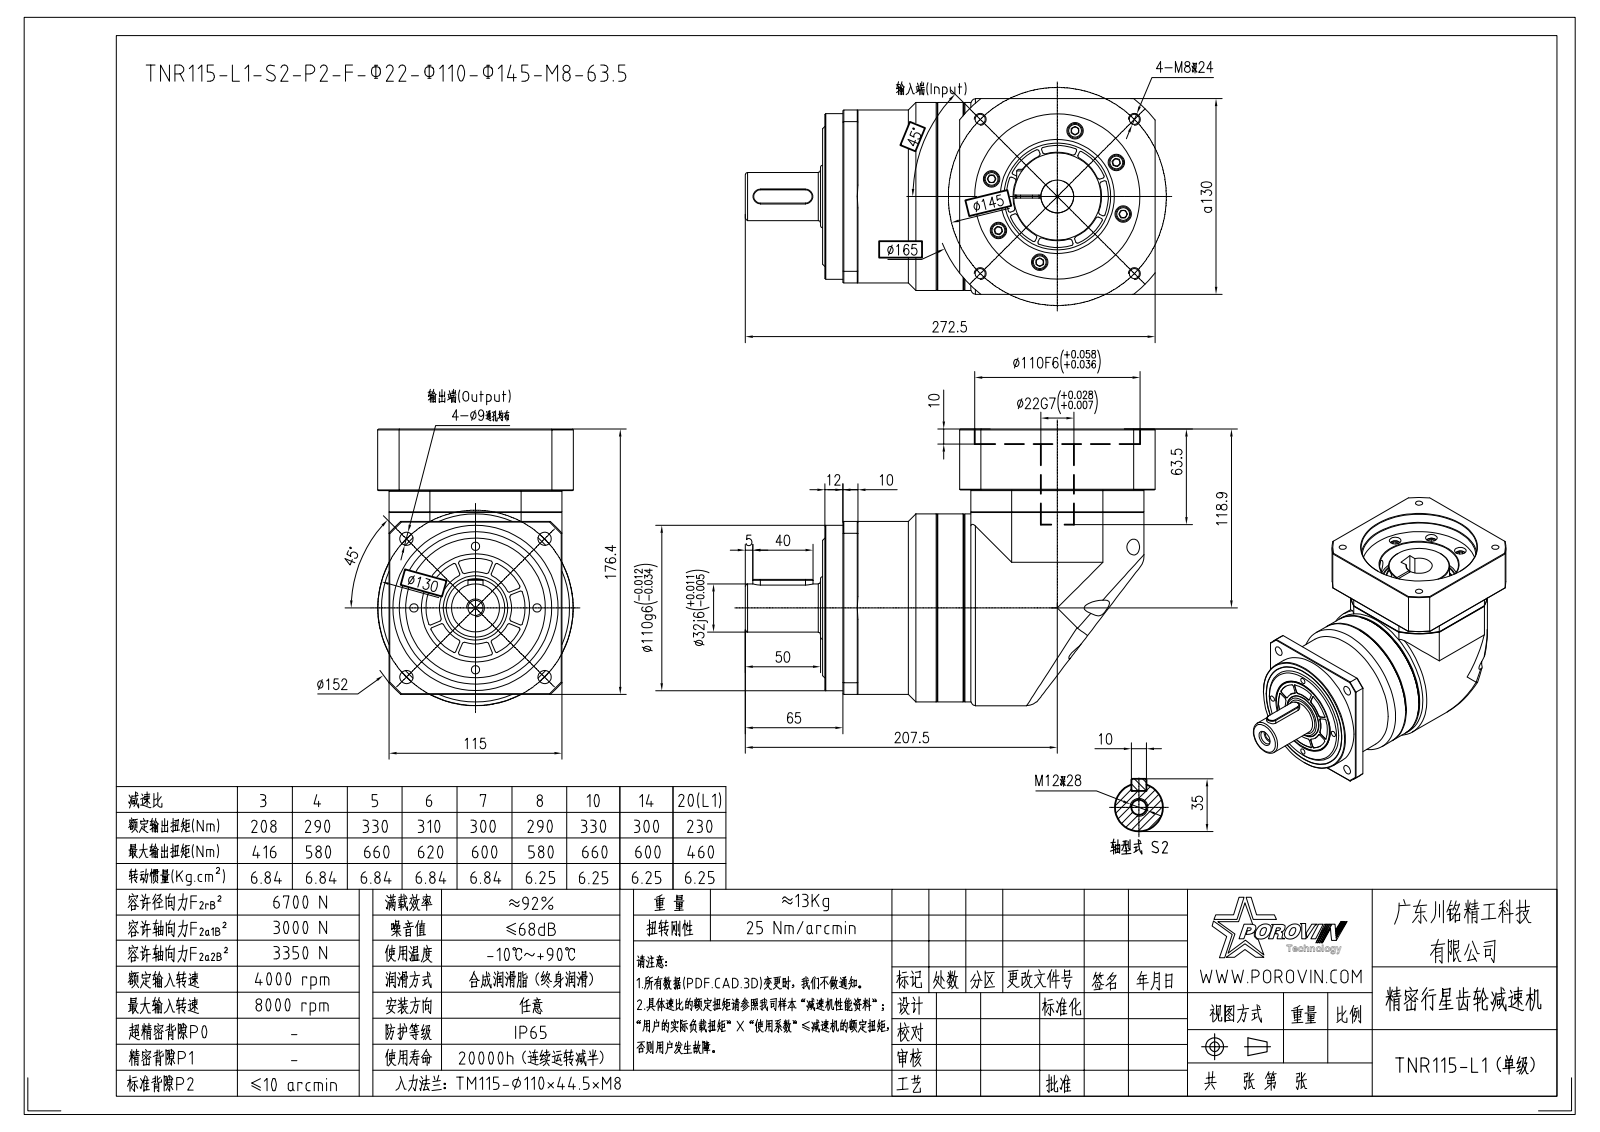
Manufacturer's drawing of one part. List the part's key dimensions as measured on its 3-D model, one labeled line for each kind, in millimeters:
Part name (STEP PRODUCT): HEXAGON_SOCKET_HEAD_CAP_SC-9367; SPRING_LOCK_WASHERS--NORMAL_TYP; HEXAGON_SOCKET_HEAD_CAP_SC-9309; HEXAGON_SOCKET_HEAD_CAP_S-29226 (+8 more)
STEP written by: CREO PARAMETRIC BY PTC INC, 2020053 (CONFIG_CONTROL_DESIGN)
Units: millimetres
Bodies: 50 solids, 1386 faces (578 planar, 557 cylindrical, 251 other)
Overall size (bounding box): 272.5 × 183.9 × 130
Volume: 2 910 000 mm³ · Surface area: 351 891 mm²
Round holes (diameter × count): ⌀6.68 ×19, ⌀6.5 ×13, ⌀11 ×12, ⌀5 ×8, ⌀10.5 ×7, ⌀6.6 ×6, ⌀6.8 ×5, ⌀5.5 ×4, ⌀9 ×4, ⌀72 ×2, ⌀8.5 ×1, ⌀10.2 ×1
Round bosses / shafts (diameter × count): ⌀10 ×19, ⌀9.88 ×19, ⌀6 ×19, ⌀130 ×1, ⌀125 ×1, ⌀124 ×1, ⌀115 ×1, ⌀110 ×1
Partial cylindrical surfaces — rounded edges, fillets, slot ends (radius × count): R1 ×64, R5 ×3, R6.75 ×1, R10 ×1, R65 ×1, R76 ×1, R82.5 ×1
Main face-to-face distances: 18, 17.8, 14.9, 7.5, 122.5, 55.4, 130, 3, 20, 40.5
Hole centre spacings: 45.25, 57.25, 46.18, 51.41, 98.8, 111.28, 91.96, 46.42
